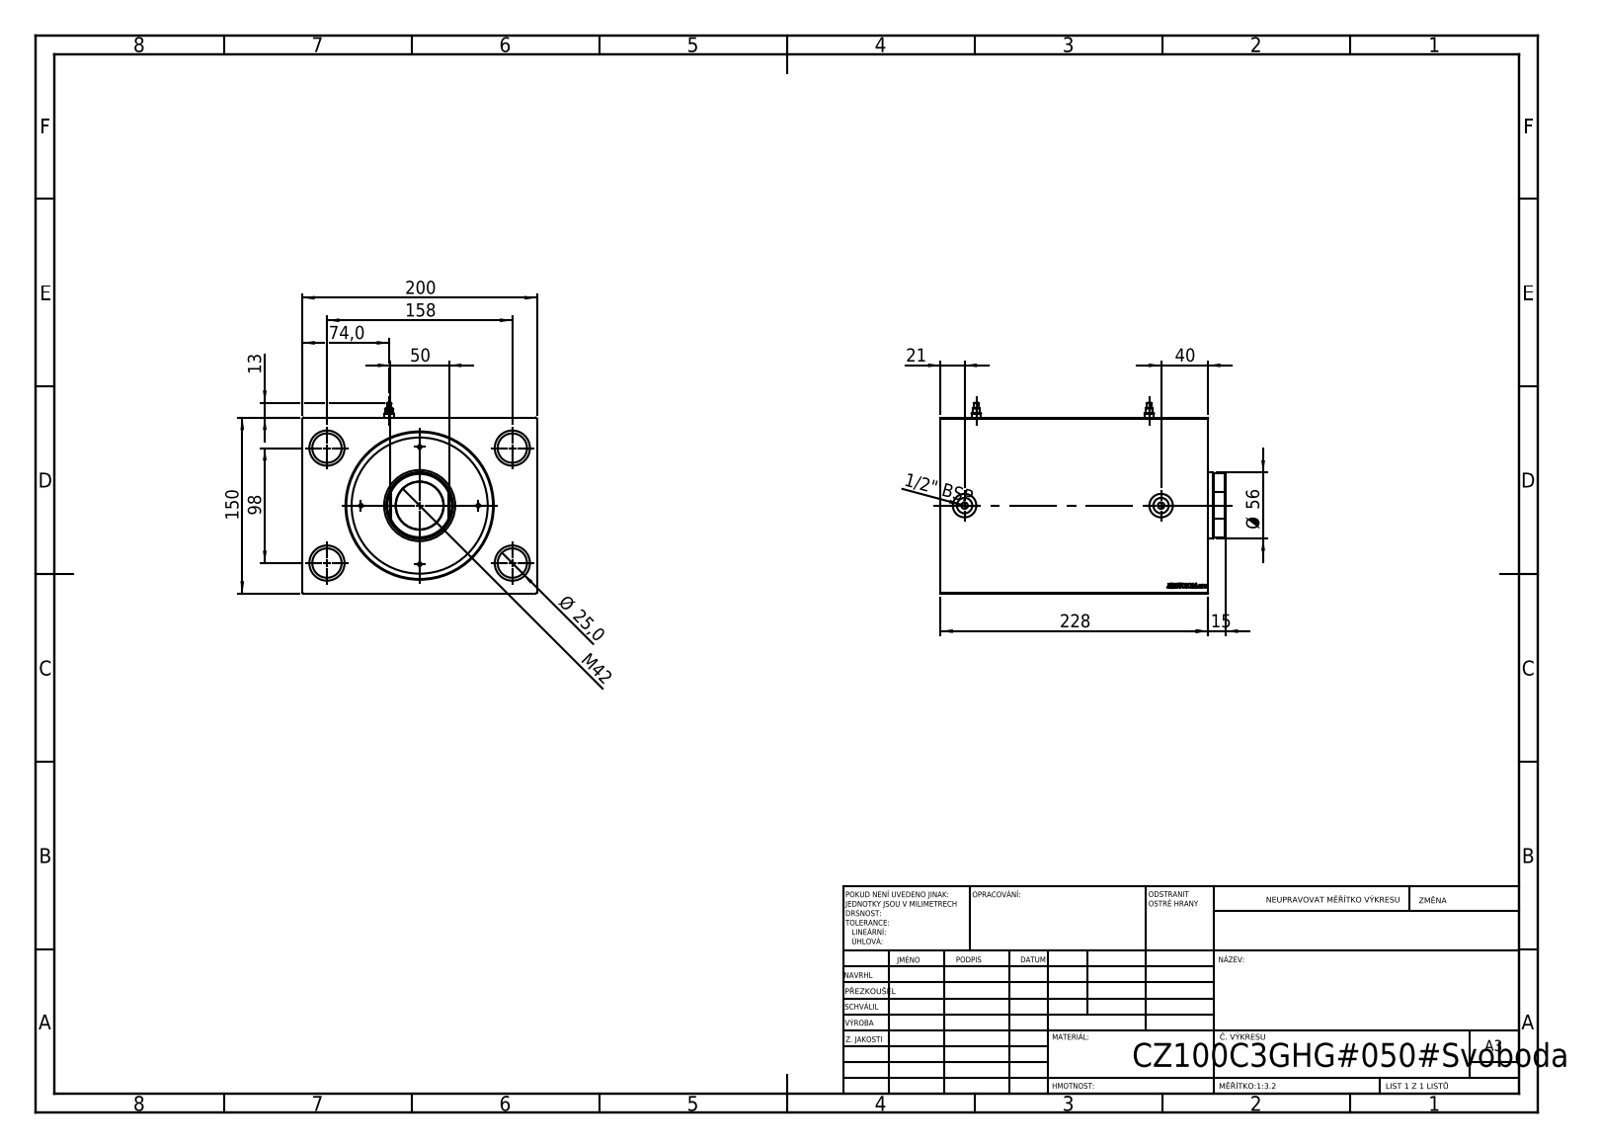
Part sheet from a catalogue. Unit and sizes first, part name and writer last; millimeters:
Units: millimetres
Overall size (bounding box): 228 × 200 × 150
Round holes (diameter × count): ⌀25 ×4, ⌀30 ×4, ⌀5.5 ×2, ⌀8 ×2, ⌀13.16 ×2, ⌀20 ×2, ⌀36 ×1, ⌀100 ×1, ⌀125 ×1
Main face-to-face distances: 150, 200, 228, 194.7, 33.3, 15, 179.7, 213, 10.33, 217.67
Hole centre spacings: 92.96, 98, 158, 185.92, 147.5, 167.5
Volume: 4 774 000 mm³ · Surface area: 351 840 mm²
Bodies: 1 solid, 825 faces (397 planar, 46 cylindrical, 382 other)
STEP written by: SolidWorks 2019 (CONFIG_CONTROL_DESIGN)
